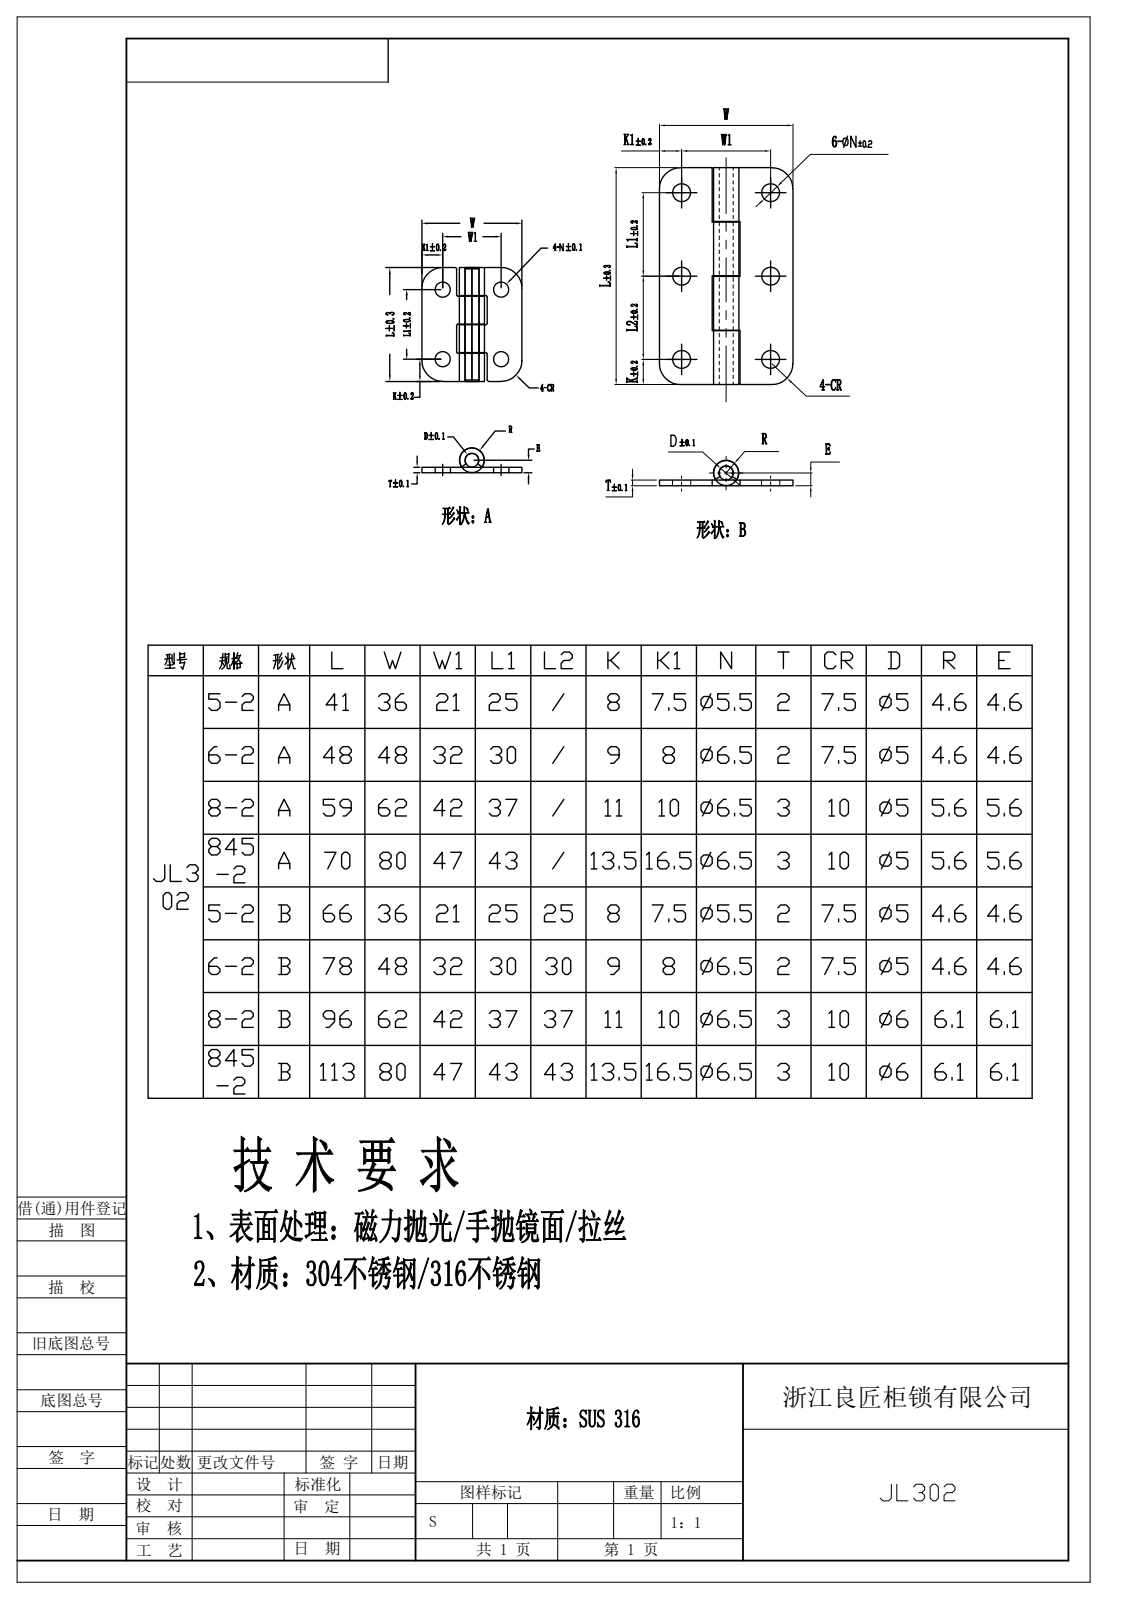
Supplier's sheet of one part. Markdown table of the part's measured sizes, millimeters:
| quantity | value |
| --- | --- |
| STEP written by | Rhino 8.5 (CONFIG_CONTROL_DESIGN) |
| units | millimeters |
| bodies | 88 solids, 1044 faces (648 planar, 232 cylindrical, 164 other) |
| overall size | 245.73 × 221.13 × 12.2 |
| volume | 123 121 mm³ |
| surface area | 107 378 mm² |
| round holes (diameter × count) | 6.5 × 30, 5.5 × 10, 5.2 × 5, 6.2 × 2, 5 × 1 |
| round bosses / shafts (diameter × count) | 9.2 × 3, 5 × 3, 12.2 × 2, 11.2 × 2, 6 × 2, 9 × 1 |
| partial cylindrical surfaces (radius × count) | 1.3 × 16, 7.5 × 16, 10 × 16, 0.5 × 8, 5.38 × 1, 7.23 × 1, 8.73 × 1, 9.21 × 1 |
| main face-to-face distances | 3, 1, 2, 6.97, 24.05, 7.97, 32.5, 47.5, 1.08, 8.97 |
| hole center spacings | 25, 30, 32.65, 43.86, 21, 32, 79.46, 82.19 |
